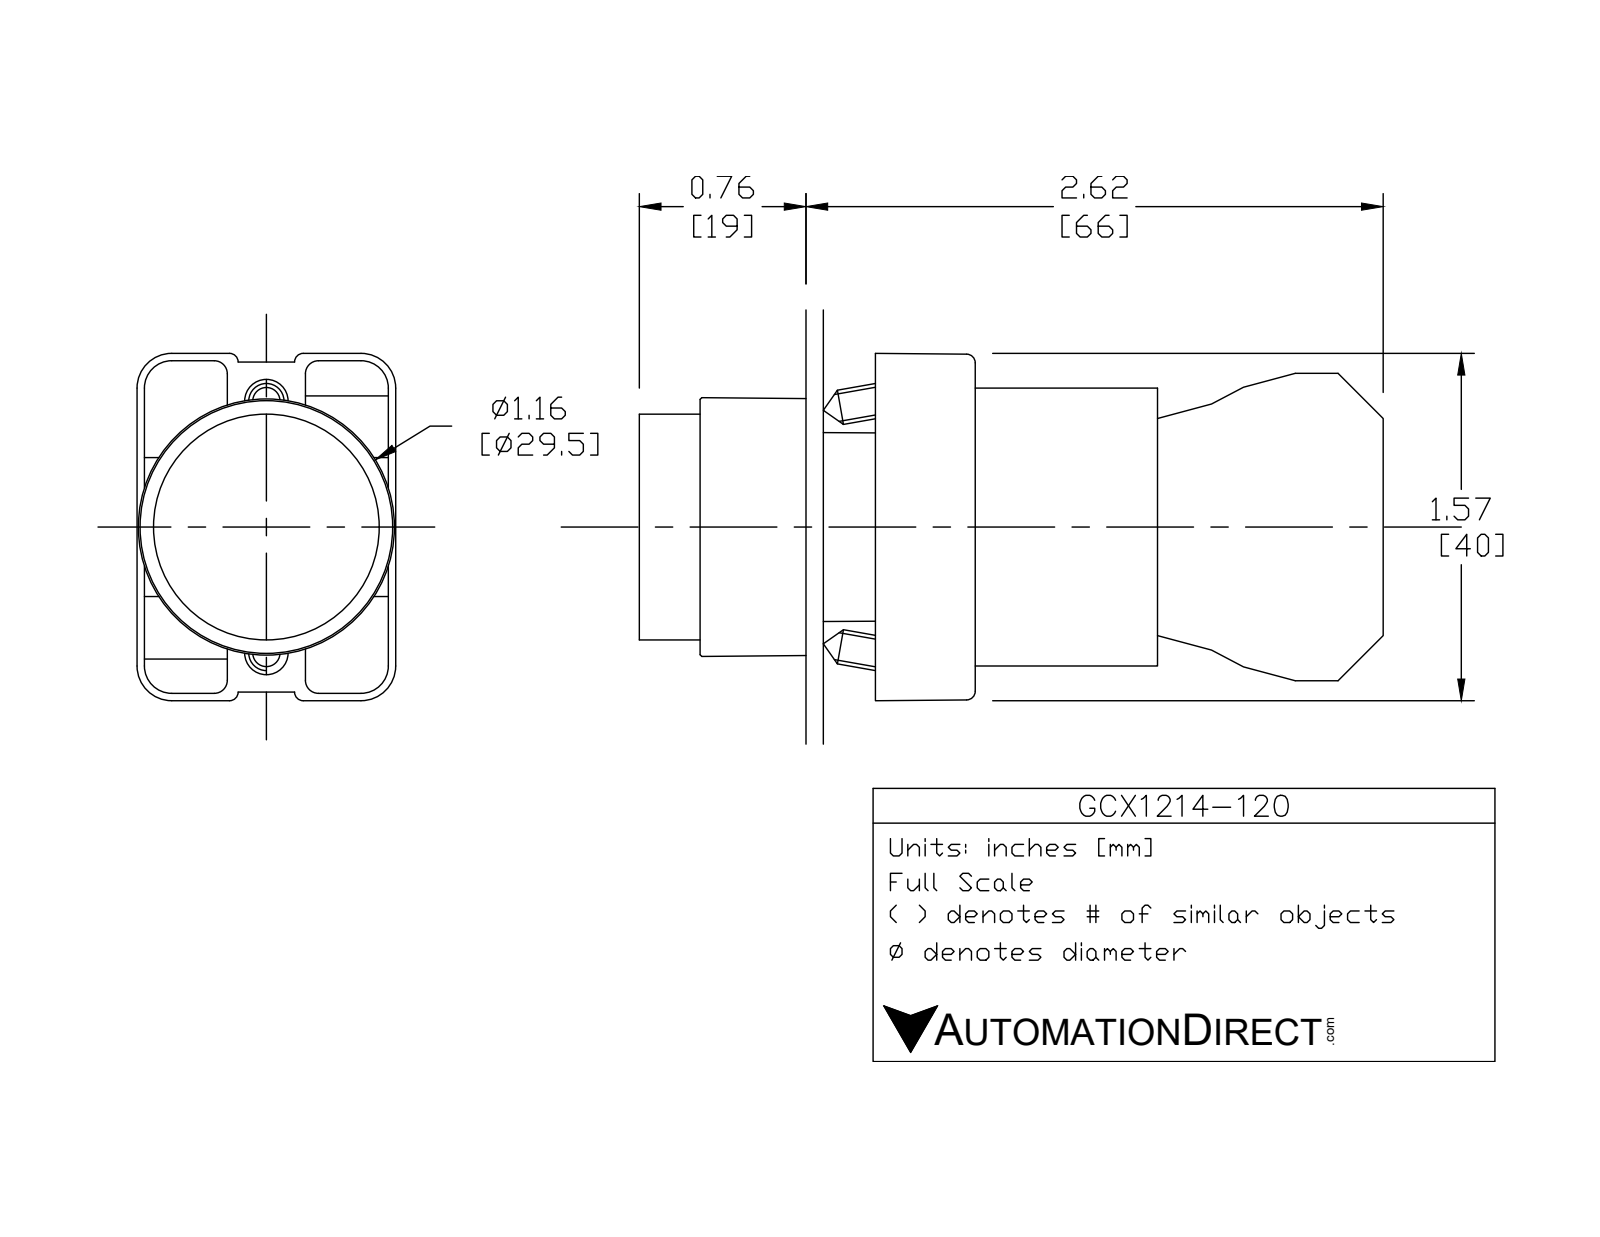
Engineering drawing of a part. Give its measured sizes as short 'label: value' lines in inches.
name: ECX1050; ecx1040; GCX1214 OPERATOR; ecx1029 (+1 more)
written by: SolidWorks 2016 (AUTOMOTIVE_DESIGN)
unit: in
bodies: 7 solids, 425 faces (250 planar, 144 cylindrical, 31 other)
size: 3.319 × 1.581 × 1.177
volume: 2.721 in³; area: 36.32 in²
holes: 2× ⌀0.079, 2× ⌀0.124, 2× ⌀0.13, 1× ⌀0.087, 1× ⌀0.197, 1× ⌀0.469, 1× ⌀0.878, 1× ⌀0.888, 1× ⌀1.024
bosses: 4× ⌀0.157, 1× ⌀1.175, 1× ⌀1.004, 1× ⌀0.945, 1× ⌀0.856, 1× ⌀0.78, 1× ⌀0.504
rounds: 24× R0.059, 12× R0.041, 12× R0.124, 12× R0.157, 8× R0.039, 2× R0.128, 1× R0.02, 1× R0.063
face distances: 0.827, 0.579, 1.171, 2.02, 1.193, 0.031, 0.033, 0.573, 1.165, 0.593
hole spacings: 0.236, 0.544, 0.472, 0.49
